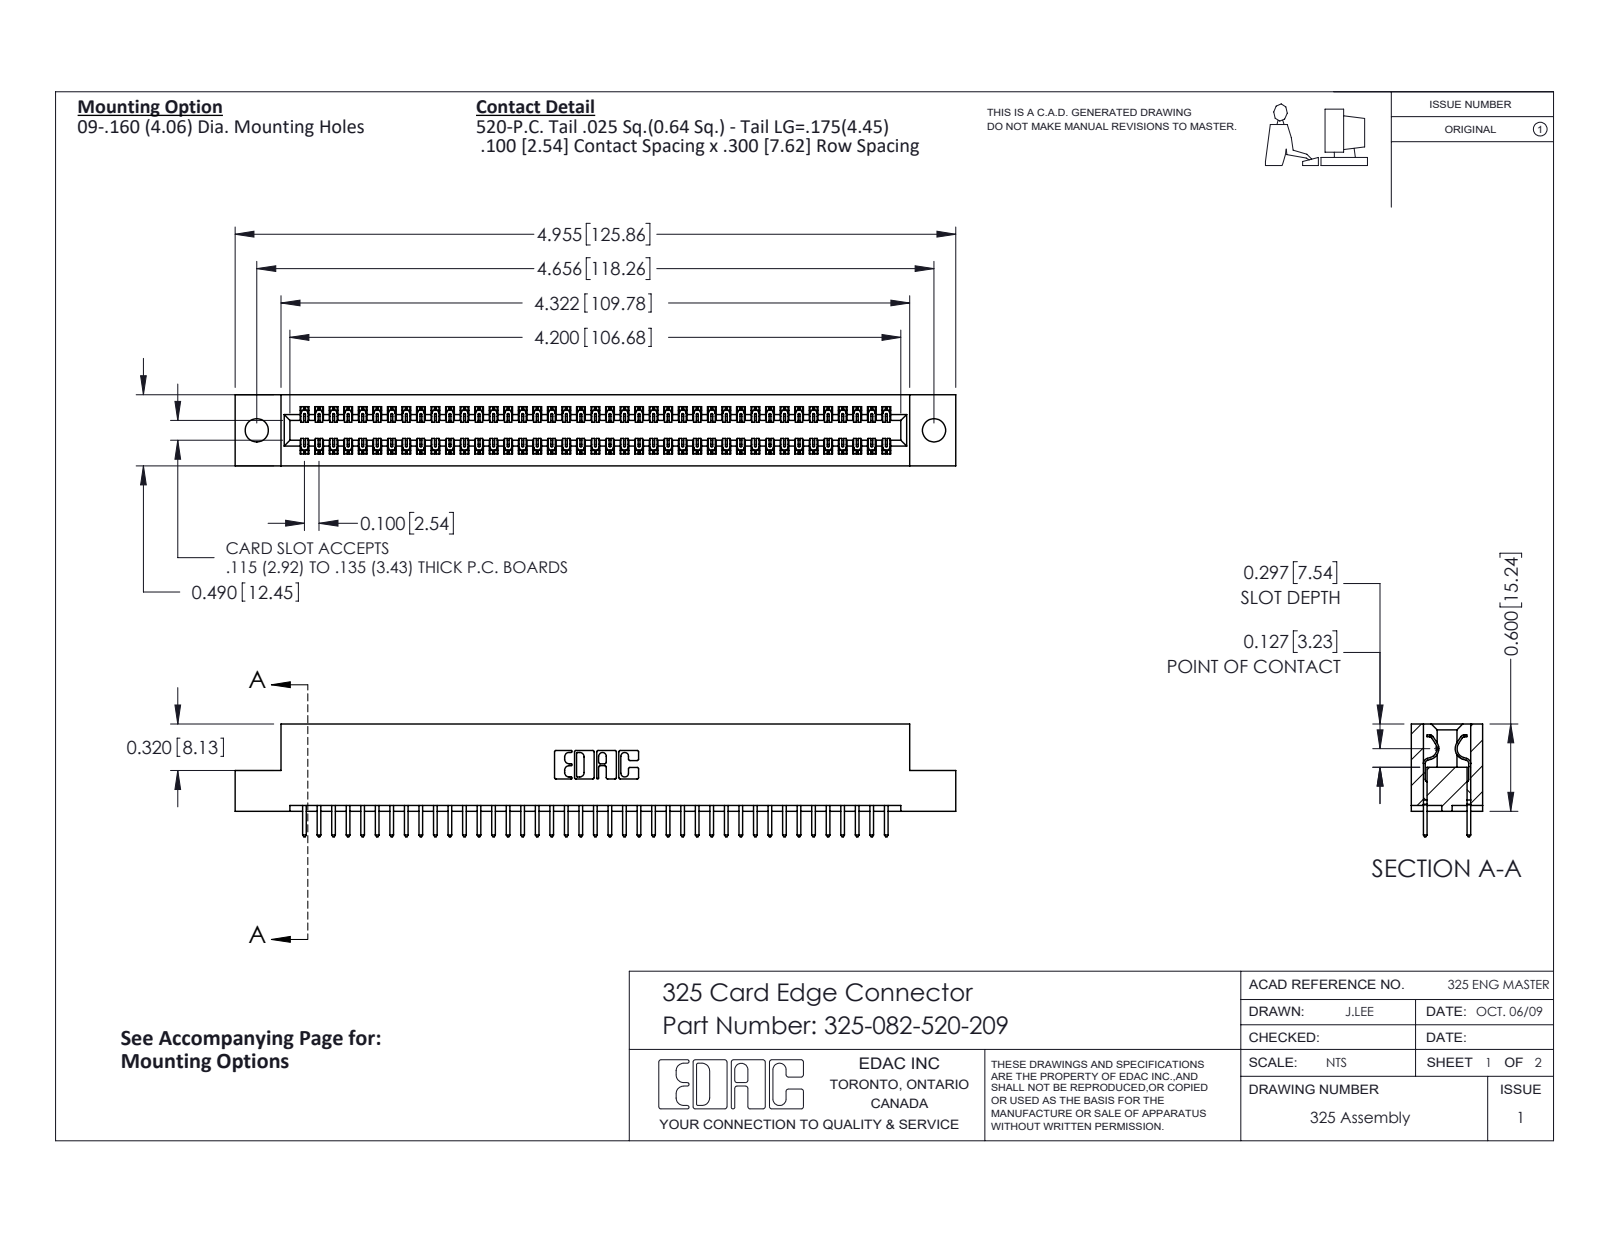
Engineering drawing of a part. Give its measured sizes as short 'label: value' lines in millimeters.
name: 325-082-520-209; 325-292-001_325-293-120; 325 Part_.160 TH
written by: SolidWorks 2016 (CONFIG_CONTROL_DESIGN)
unit: mm
bodies: 83 solids, 4378 faces (3022 planar, 1356 cylindrical, 0 other)
size: 125.9 × 19.7 × 12.4
volume: 16 000 mm³; area: 19 090 mm²
holes: 2× ⌀4.1
rounds: 123× R0.2, 82× R0.3, 22× R0.3, 6× R0.2, 6× R0.8, 3× R0.7, 2× R0.4, 2× R0.6
face distances: 2.1, 10.3, 7.6, 12.4, 2.7, 9.7, 0.6, 8.3, 7, 14.2
hole spacings: 118.3
